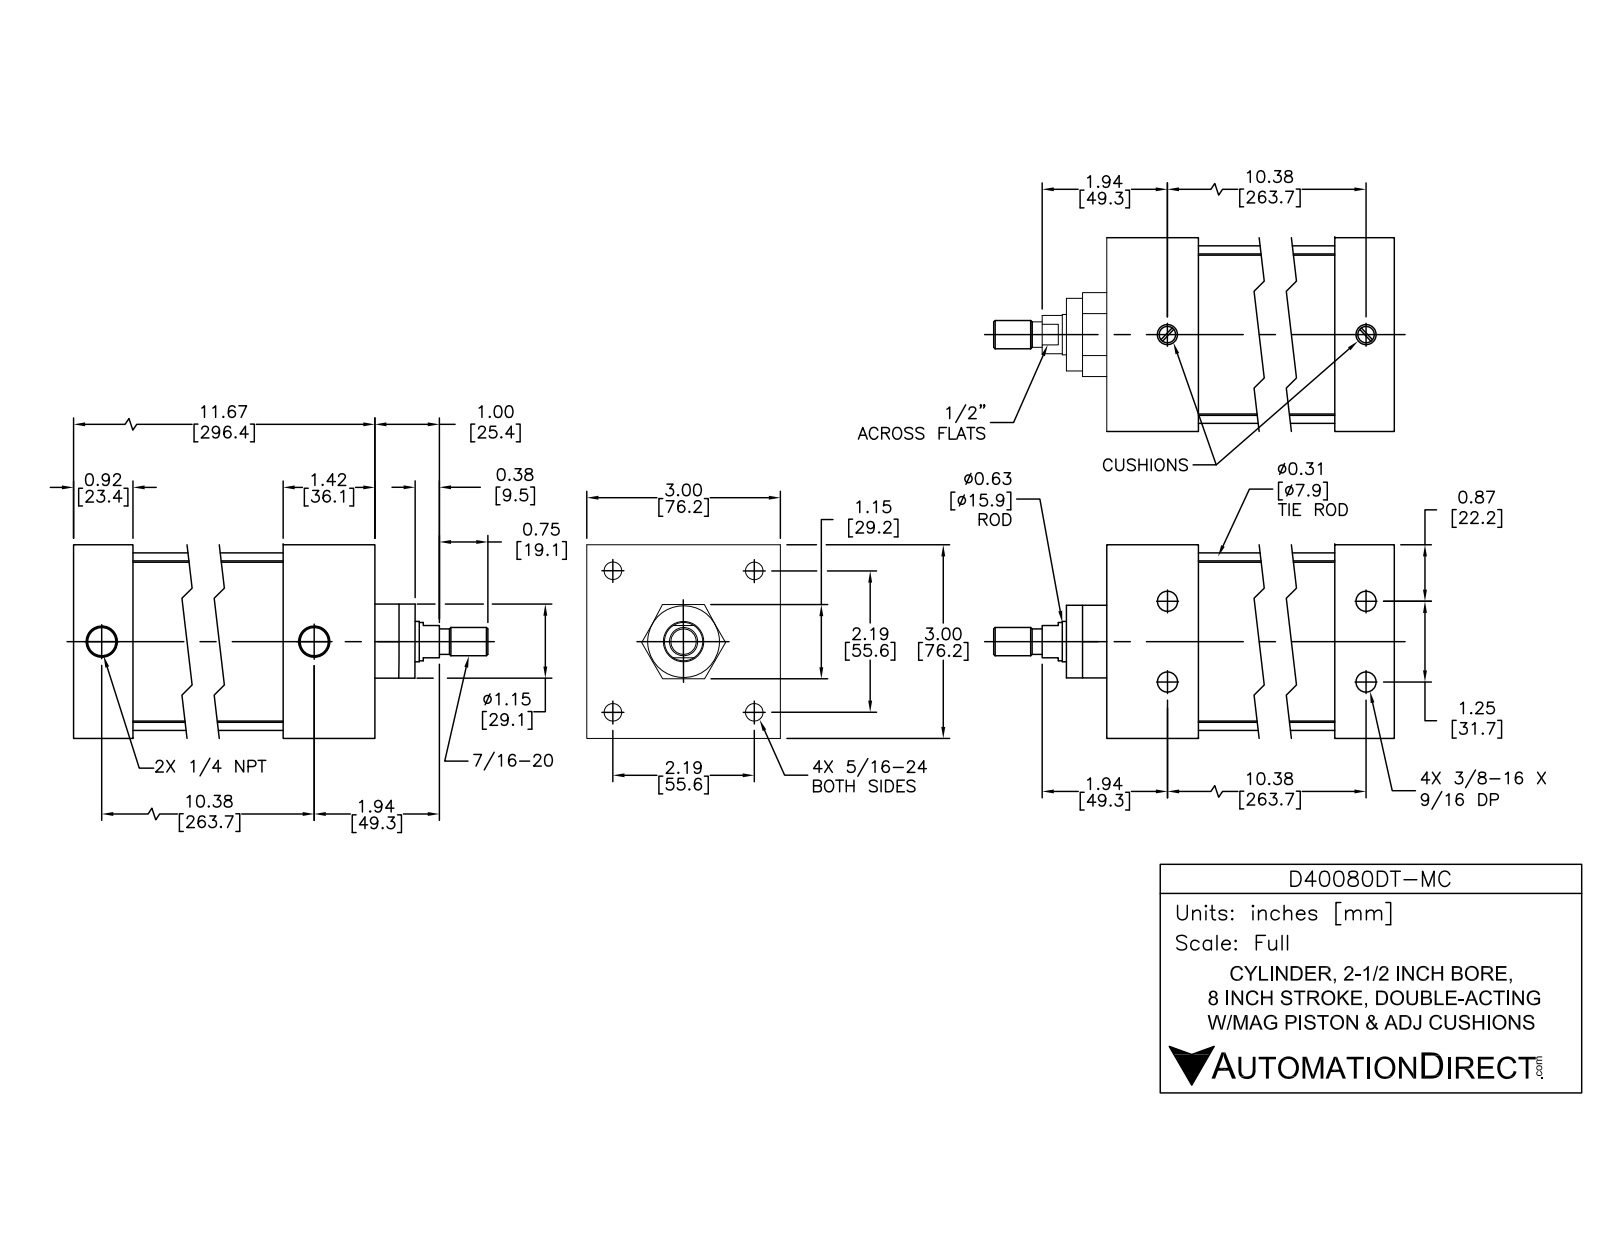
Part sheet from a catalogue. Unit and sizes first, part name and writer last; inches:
Units: inches
Overall size (bounding box): 13.496 × 3 × 3
Round holes (diameter × count): ⌀0.267 ×4, ⌀0.307 ×4, ⌀0.359 ×4, ⌀0.5 ×4, ⌀0.297 ×2, ⌀0.477 ×2, ⌀0.625 ×1, ⌀0.628 ×1, ⌀2.5 ×1
Round bosses / shafts (diameter × count): ⌀0.484 ×4, ⌀0.313 ×4, ⌀0.282 ×4, ⌀2.75 ×1, ⌀2.497 ×1, ⌀1.12 ×1, ⌀0.622 ×1, ⌀0.59 ×1
Partial cylindrical surfaces — rounded edges, fillets, slot ends (radius × count): R0.3 ×4
Main face-to-face distances: 3, 0.08, 9.326, 11.746, 10.726, 1.02, 1.42, 9.306, 10.326, 1
Hole centre spacings: 1.556, 2.2, 10.389, 10.37, 0.625, 0.625, 1.25, 3.111
Volume: 41.89 in³ · Surface area: 328.6 in²
Bodies: 12 solids, 298 faces (94 planar, 114 cylindrical, 90 other)
Part name (STEP PRODUCT): D40080DT-MC; D40080DT-M PISTON; D40080DT-M BODY
STEP written by: SolidWorks 2015 (AUTOMOTIVE_DESIGN)
